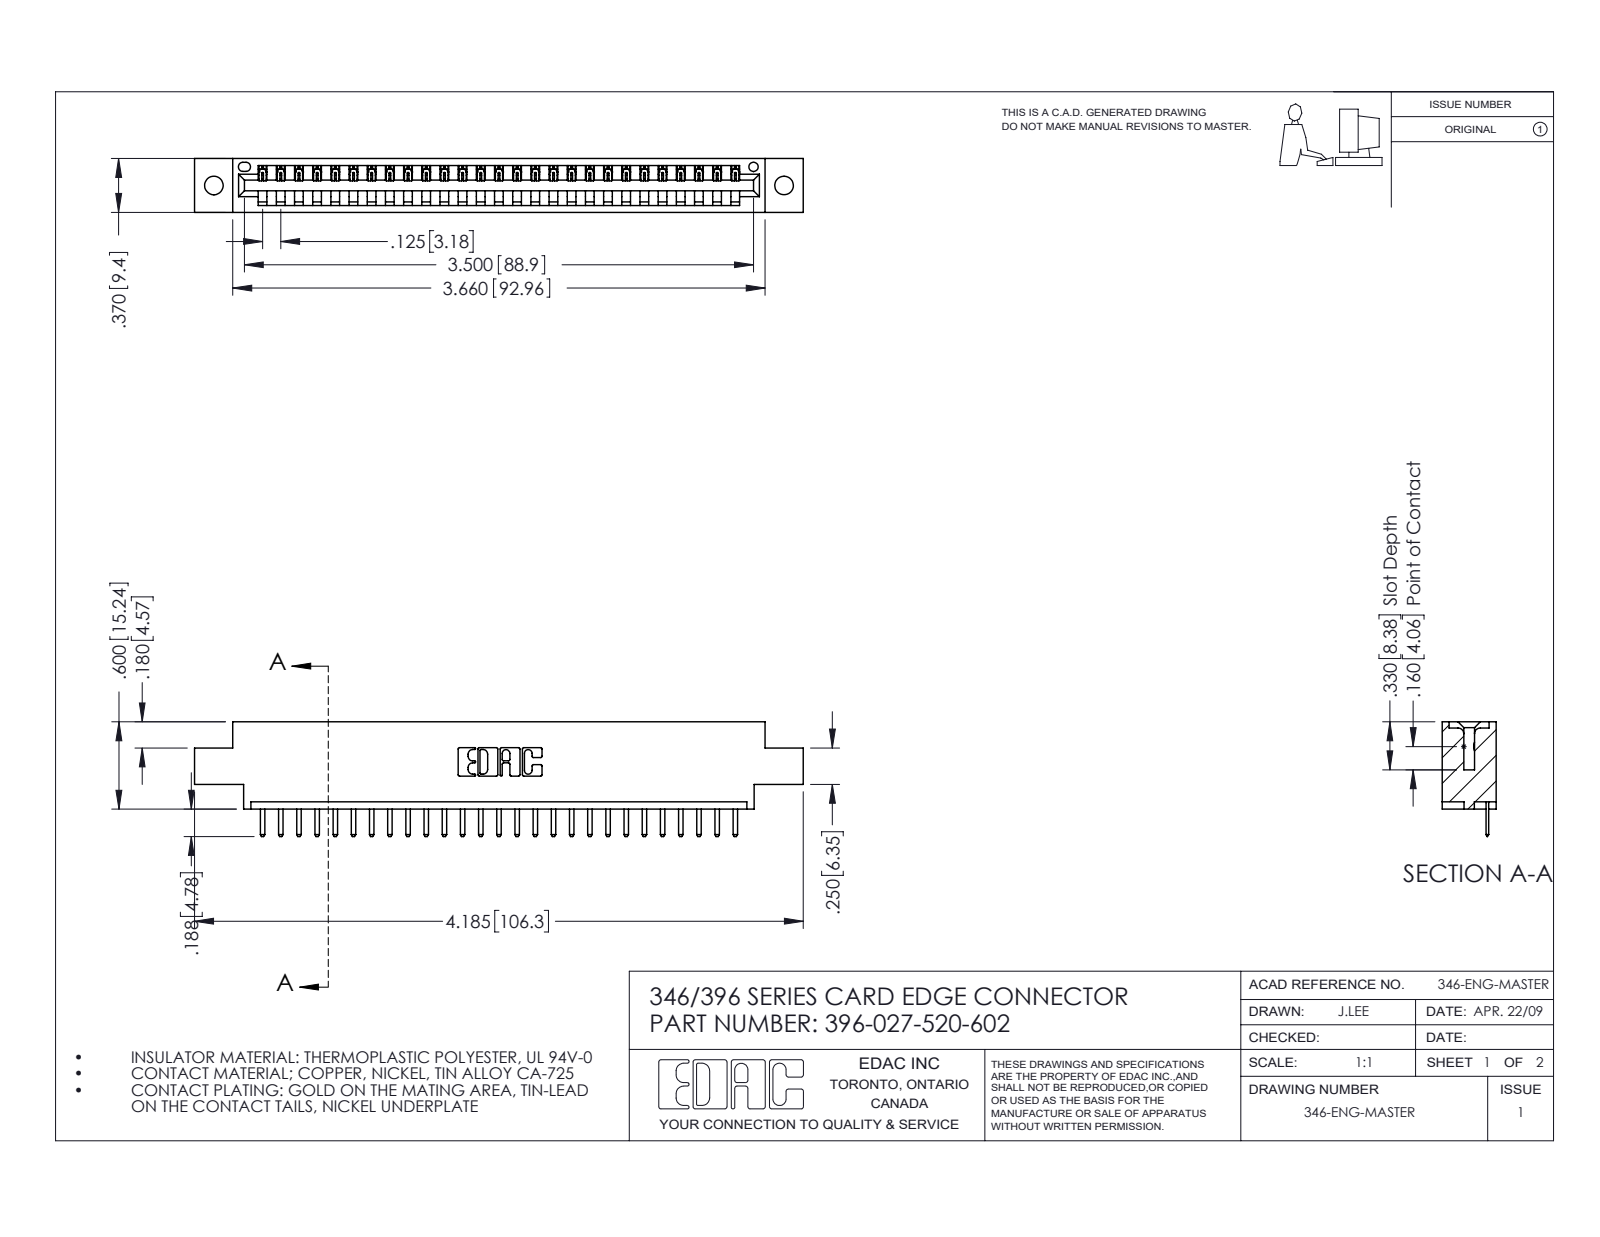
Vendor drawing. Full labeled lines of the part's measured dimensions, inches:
Part name (STEP PRODUCT): 396-027-520-602; 345-292-001_345-293-120; 346 Part_0.170 Offset - 0.128 Dia
STEP written by: SolidWorks 2016 (CONFIG_CONTROL_DESIGN)
Units: inches
Bodies: 28 solids, 1800 faces (1214 planar, 586 cylindrical, 0 other)
Overall size (bounding box): 4.185 × 0.788 × 0.37
Volume: 0.598 in³ · Surface area: 18.17 in²
Round holes (diameter × count): ⌀0.128 ×2, ⌀0.064 ×1
Partial cylindrical surfaces — rounded edges, fillets, slot ends (radius × count): R0.01 ×56, R0.006 ×54, R0.01 ×22, R0.007 ×6, R0.031 ×6, R0.026 ×3, R0.031 ×2, R0.04 ×2
Main face-to-face distances: 0.048, 0.322, 0.37, 0.25, 0.148, 0.222, 0.1, 0.174, 0.072, 0.298
Hole centre spacings: 0.246, 3.712, 3.92
